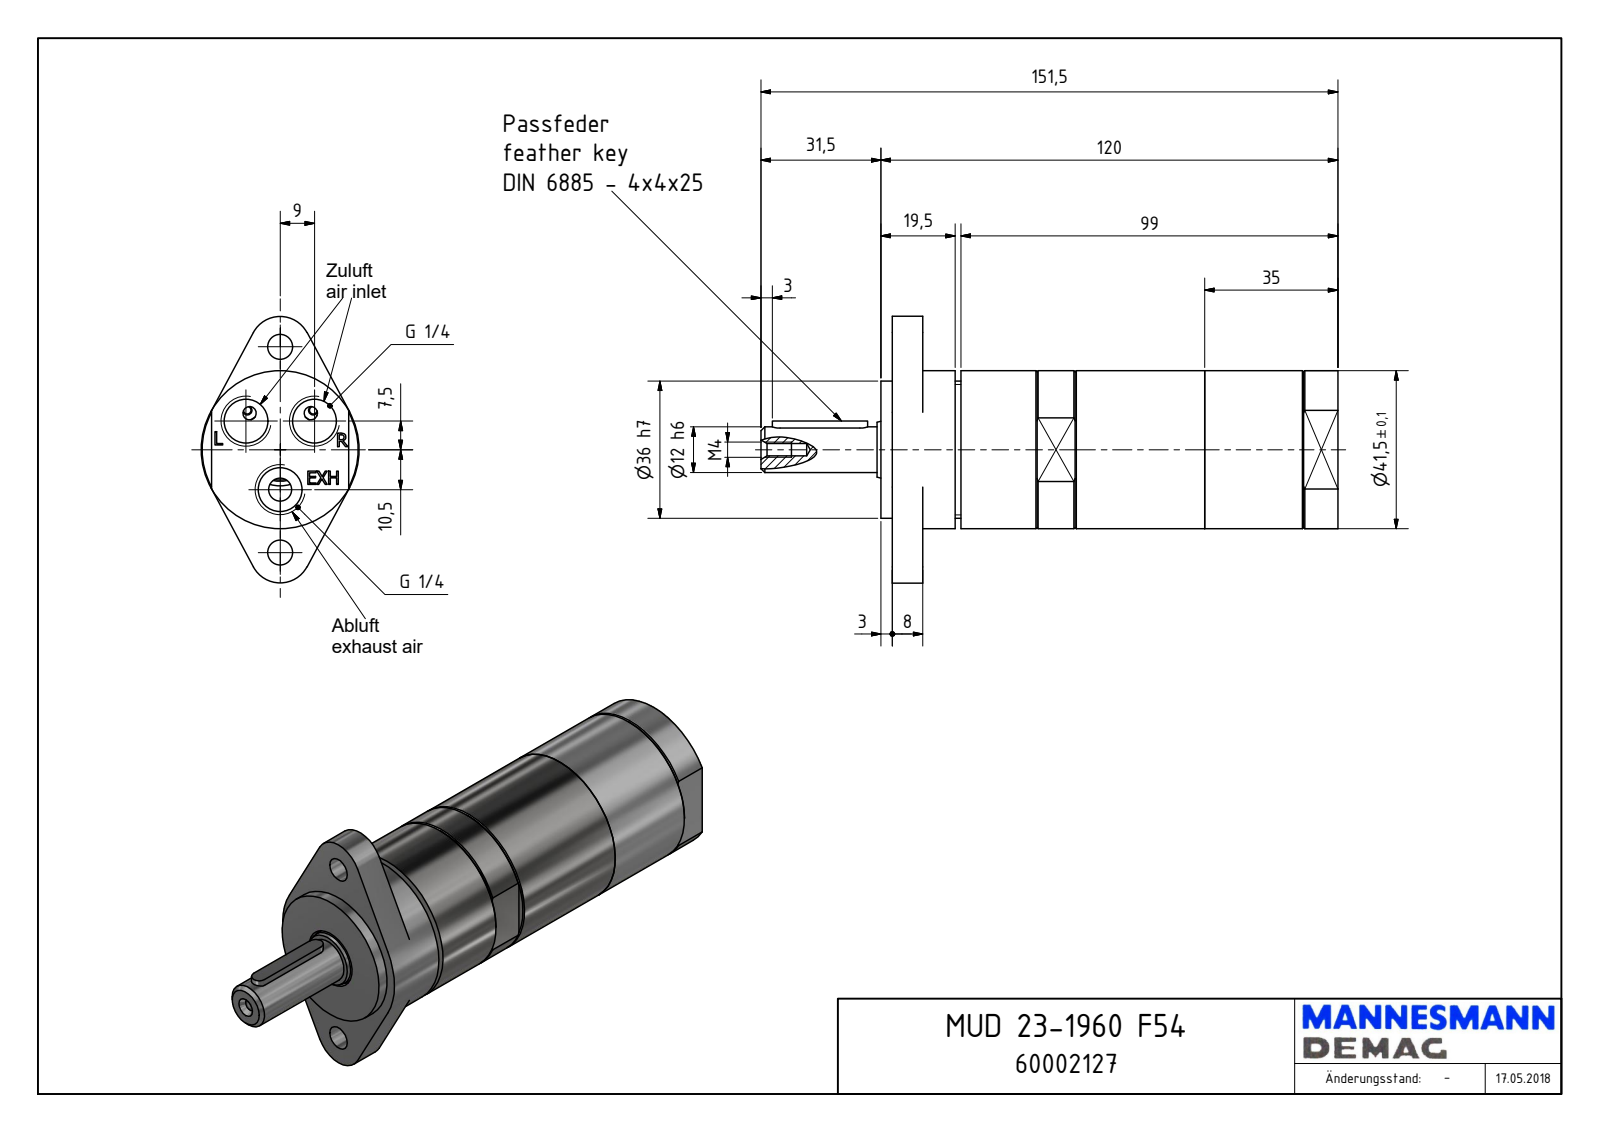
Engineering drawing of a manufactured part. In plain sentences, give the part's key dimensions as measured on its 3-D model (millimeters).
The part is named "MUD 23-1960_60002127". Its 3-D file was written by "Autodesk Inventor 2018 (AUTOMOTIVE_DESIGN)". It is 1 solid with 135 faces: 89 planar, 23 cylindrical and 23 other. Overall it measures 151.5 by 70 by 41.5 millimeters. Its volume is 164 256 cubic millimeters and its surface area 23 250 square millimeters. Round holes: 3 of diameter 11.45, 2 of diameter 6.5, 1 of diameter 3.24, 1 of diameter 16. Round bosses or shafts: 1 of diameter 41.5, 1 of diameter 36, 1 of diameter 14.95, 1 of diameter 12. Partial cylindrical surfaces (rounded edges, fillets, slot ends): 2 of radius 2, 2 of radius 8. The main face-to-face distances are 117, 3, 120, 11, 8, 109, 21, 1, 41.48, 10. The hole center spacings are 11.72, 20.12, 21.48, 27, 35.65, 10.5, 16.5, 18.
